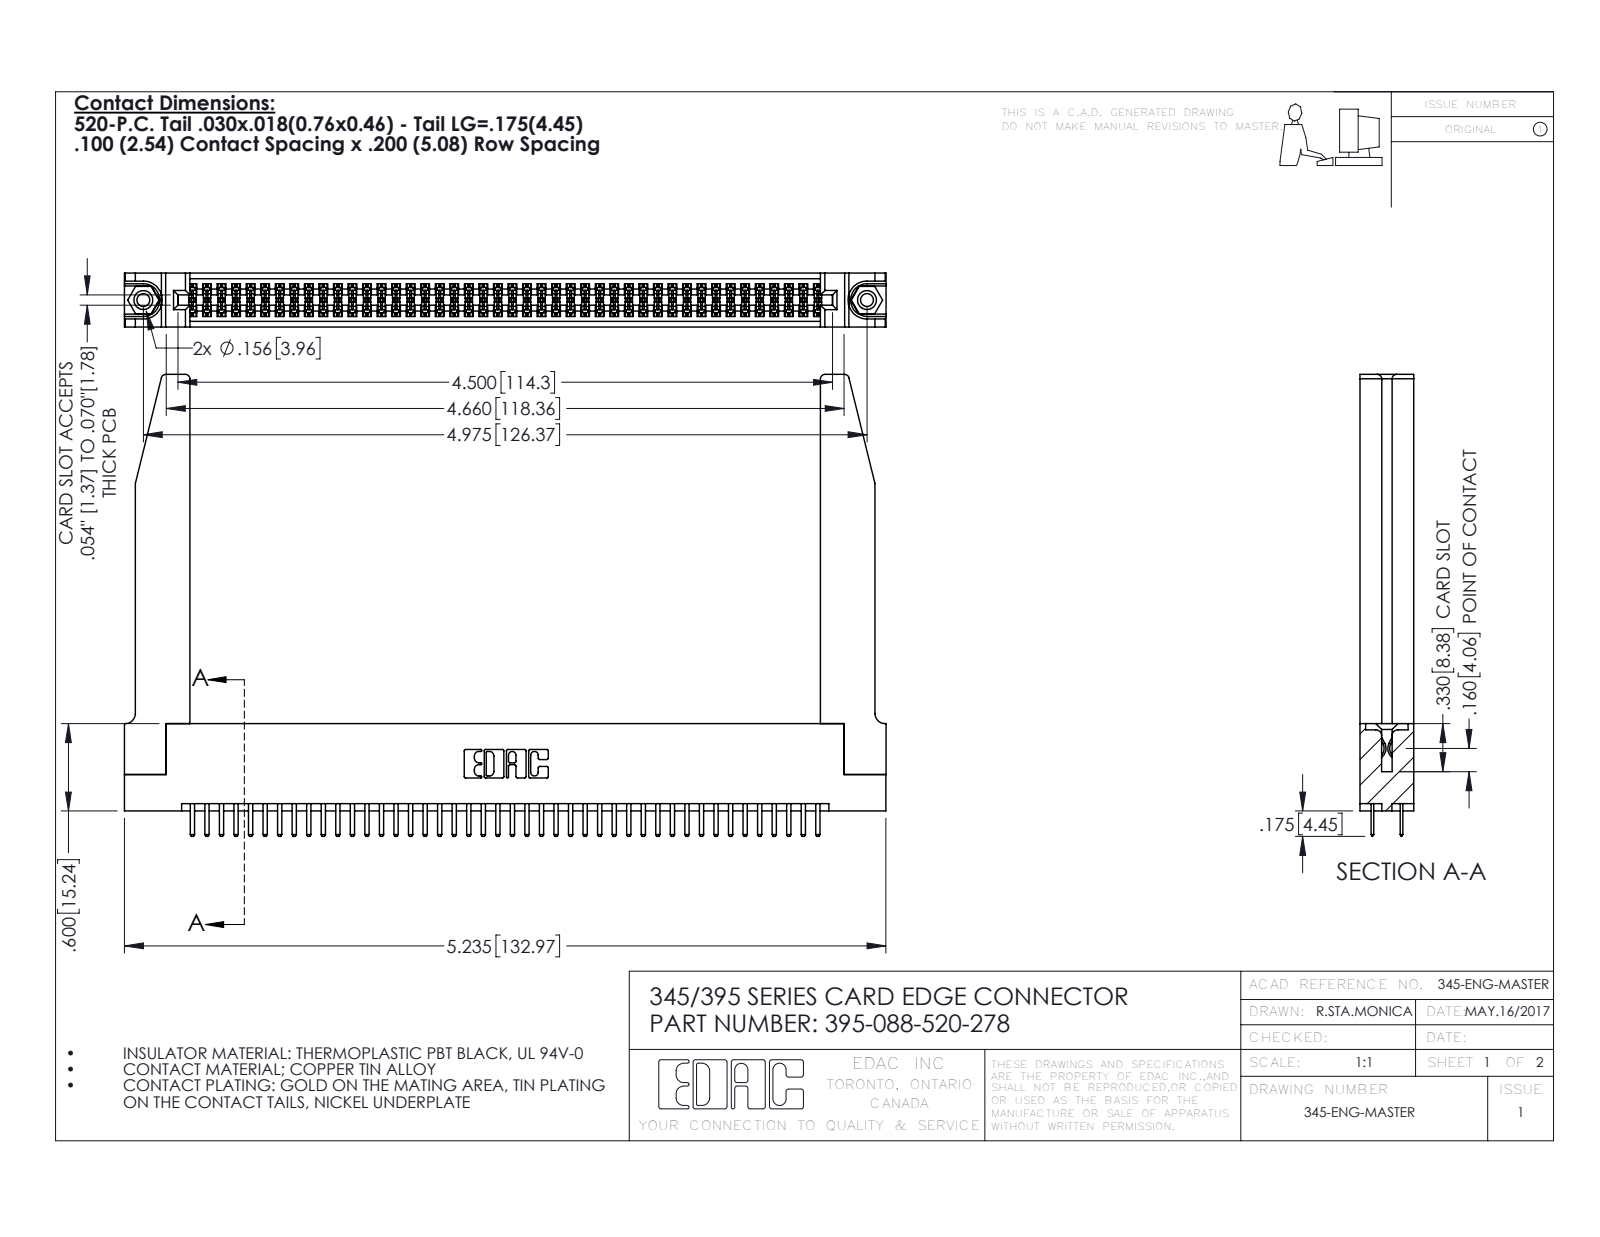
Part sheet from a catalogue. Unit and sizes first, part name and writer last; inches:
Units: inches
Overall size (bounding box): 5.236 × 3.175 × 0.37
Round holes (diameter × count): ⌀0.089 ×2, ⌀0.125 ×2, ⌀0.156 ×2, ⌀0.064 ×1
Round bosses / shafts (diameter × count): ⌀0.155 ×2
Partial cylindrical surfaces — rounded edges, fillets, slot ends (radius × count): R0.006 ×132, R0.01 ×92, R0.01 ×22, R0.03 ×8, R0.007 ×6, R0.031 ×6, R0.026 ×3, R0.014 ×2
Main face-to-face distances: 0.37, 0.072, 0.298, 0.2, 0.098, 0.272, 0.025, 0.225, 0.022, 0.072
Hole centre spacings: 0.27, 4.739, 4.975
Volume: 1.261 in³ · Surface area: 40.09 in²
Bodies: 93 solids, 5112 faces (3302 planar, 1758 cylindrical, 52 other)
Part name (STEP PRODUCT): 345-220-078_345-220-078; 345 Part_Flush Mounting Lugs - 0.156 Dia-TH; 345-250-001_345-250-001-102; 395-088-520-278 (+1 more)
STEP written by: SolidWorks 2016 (CONFIG_CONTROL_DESIGN)
